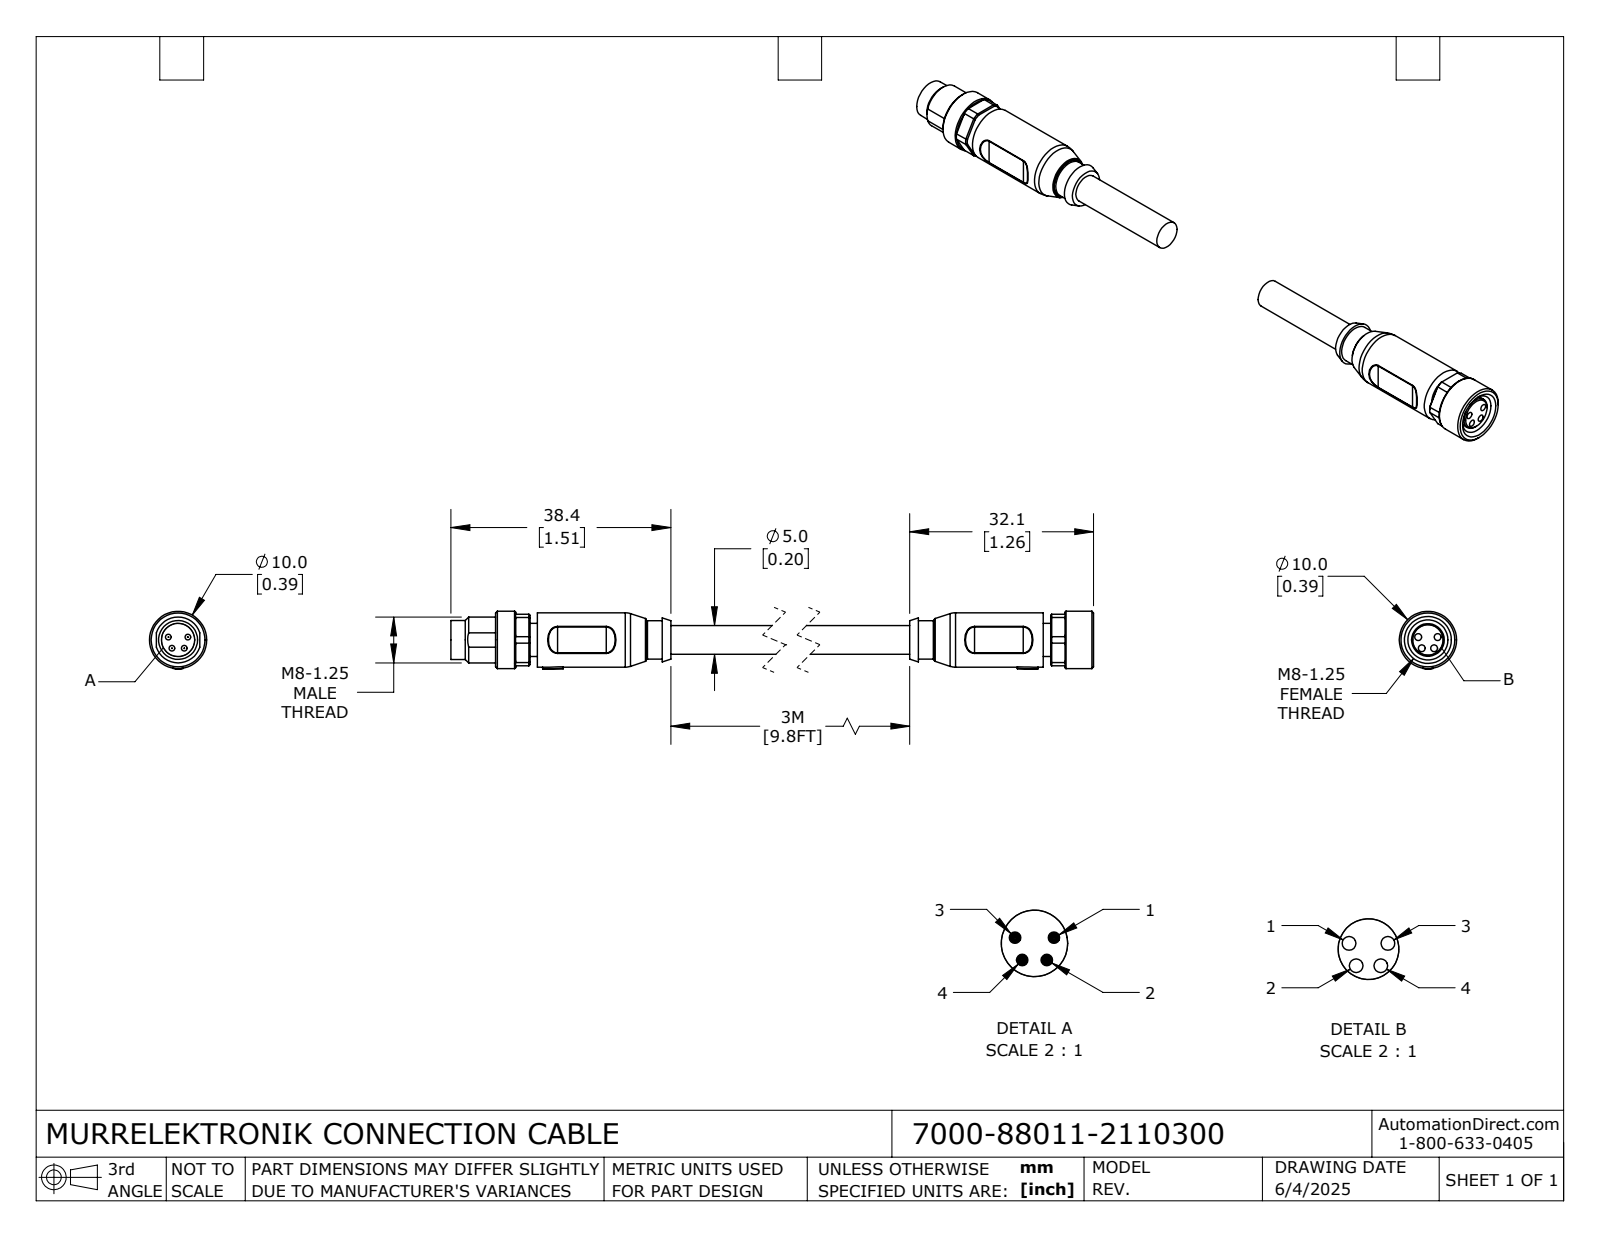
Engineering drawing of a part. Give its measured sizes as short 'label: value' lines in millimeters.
name: 7000-88011-2110300_MALE; 7000-88011-2110300_FEMALE; 7000-88011-2110300
written by: SolidWorks 2024 (CONFIG_CONTROL_DESIGN)
unit: mm
bodies: 2 solids, 226 faces (70 planar, 88 cylindrical, 68 other)
size: 135.5 × 10.05 × 10
volume: 4 815 mm³; area: 3 452 mm²
holes: 4× ⌀1.2, 1× ⌀7
bosses: 4× ⌀1, 1× ⌀10, 1× ⌀9.5, 1× ⌀8, 1× ⌀6.8, 1× ⌀6.7, 1× ⌀5.8, 1× ⌀5.7
rounds: 8× R2.5, 4× R0.2, 1× R4.9, 1× R5.05
face distances: 8.3, 1.3, 112.9, 9, 121.7, 111.6, 24.6, 8.8, 44.6, 69.6
hole spacings: 1.77, 2.05, 3.4, 1.8, 1.81, 2.15, 3.39
